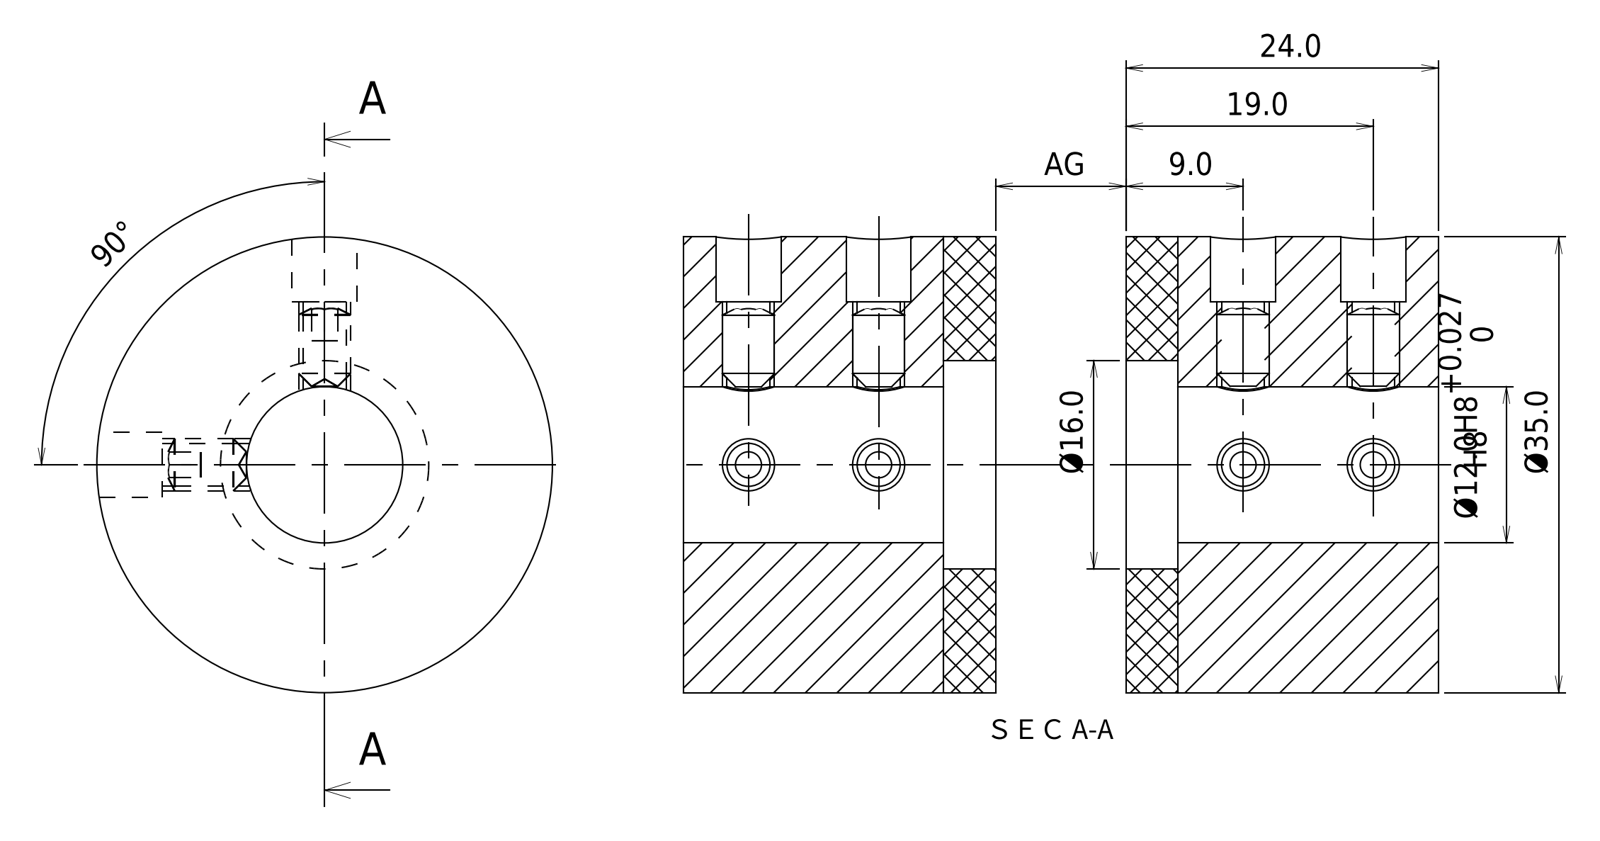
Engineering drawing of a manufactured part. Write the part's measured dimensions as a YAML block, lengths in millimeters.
step_written_by: "PSStep 10.0 (CONFIG_CONTROL_DESIGN)"
units: millimeters
bodies: {solids: 8, faces: 86, planar: 50, cylindrical: 18, other: 18}
overall_size: [35, 35, 24]
volume: 19761
surface_area: 7954
round_holes:
  - {diameter: 3.3, count: 4}
  - {diameter: 5, count: 4}
  - {diameter: 12, count: 1}
  - {diameter: 16, count: 1}
round_bosses_or_shafts:
  - {diameter: 4, count: 4}
  - {diameter: 35, count: 1}
face_to_face_distances: [20, 24, 4, 2, 8.66, 2.97, 6.66, 10.66, 11.5, 13.5]
hole_center_spacings: [10]
